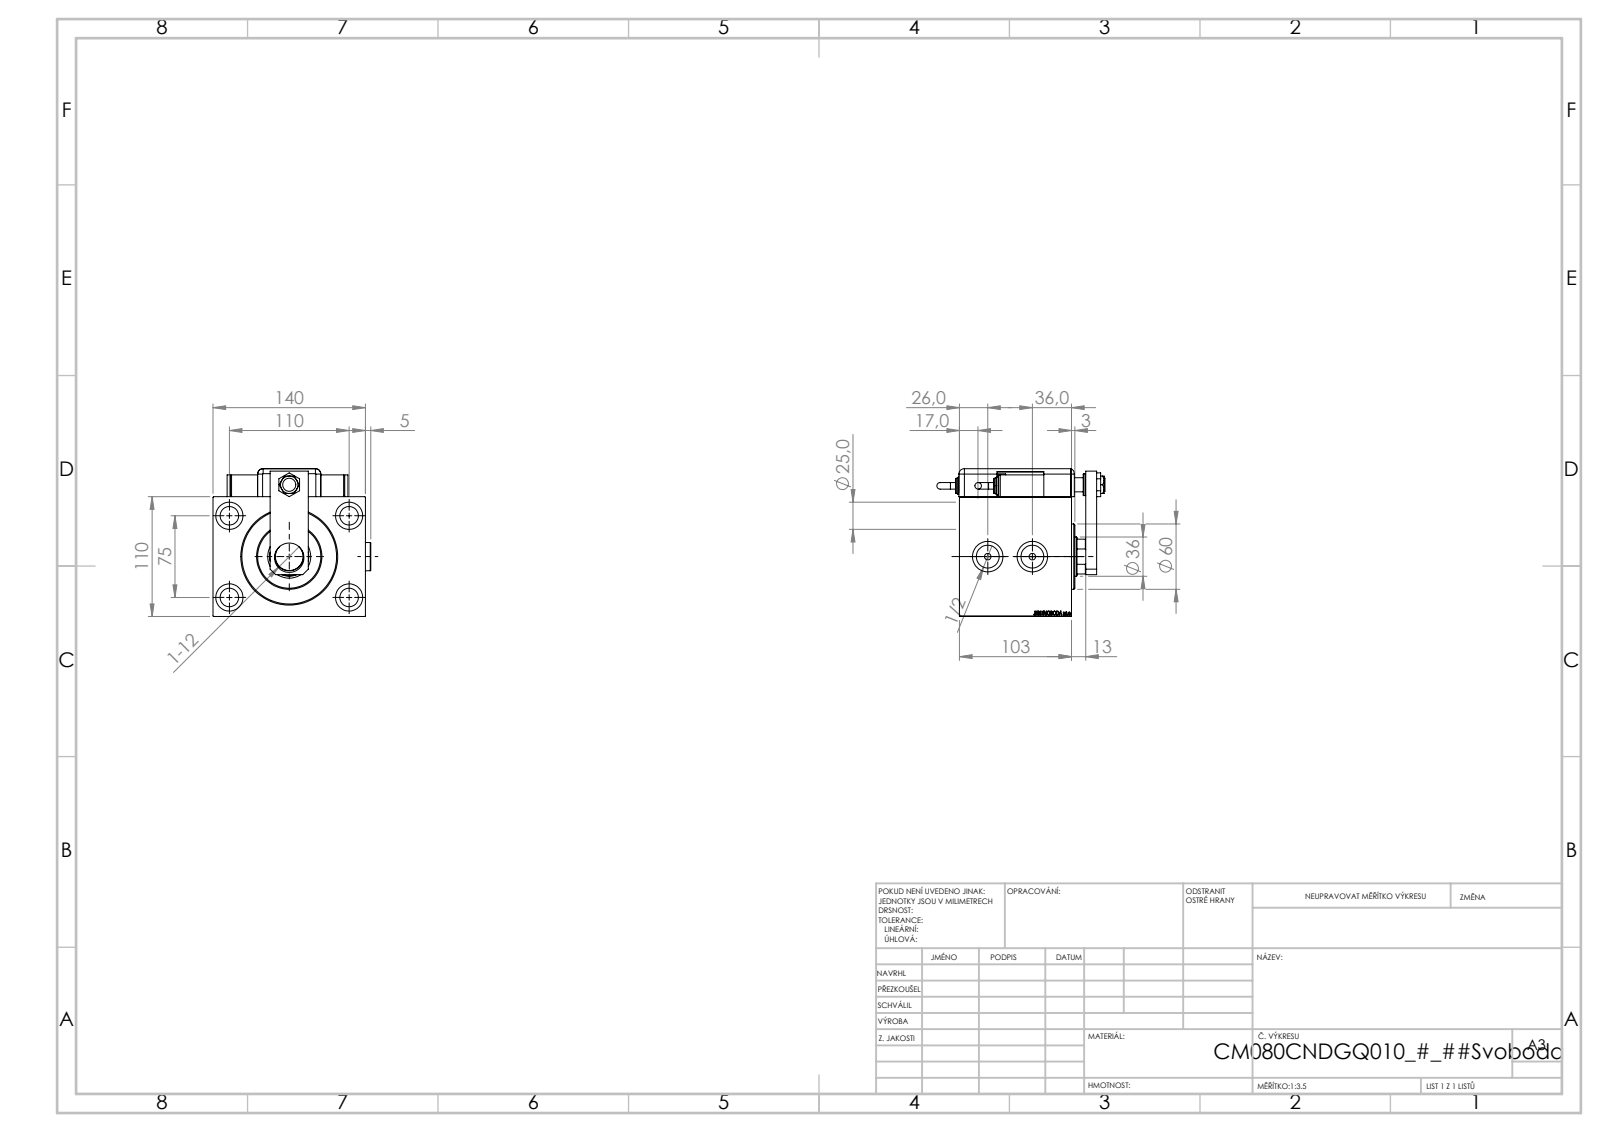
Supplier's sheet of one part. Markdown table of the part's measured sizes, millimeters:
| quantity | value |
| --- | --- |
| part name | TYC; Zatka_OIL_PORT; V450CM_C_Body; SWITCH Q (+7 more) |
| STEP written by | SolidWorks 2019 (CONFIG_CONTROL_DESIGN) |
| units | millimeters |
| bodies | 15 solids, 1301 faces (649 planar, 131 cylindrical, 521 other) |
| overall size | 154.46 × 144.9 × 135.8 |
| volume | 1 553 000 mm³ |
| surface area | 227 320 mm² |
| round holes (diameter × count) | 17 × 4, 25 × 4, 4 × 2, 6 × 2, 8 × 2, 20.96 × 2, 28 × 2, 12 × 1, 13 × 1, 14 × 1, 25.5 × 1, 27 × 1 |
| round bosses / shafts (diameter × count) | 20 × 3, 26 × 2, 16 × 2, 14 × 2, 6 × 2, 60 × 1 |
| partial cylindrical surfaces (radius × count) | 5 × 9, 10 × 1, 17.5 × 1 |
| main face-to-face distances | 110, 103, 52, 3, 51, 140, 10, 44.6, 20, 13 |
| hole center spacings | 66.57, 61.95, 66.01, 67.14, 75, 110, 117.21, 133.14 |
